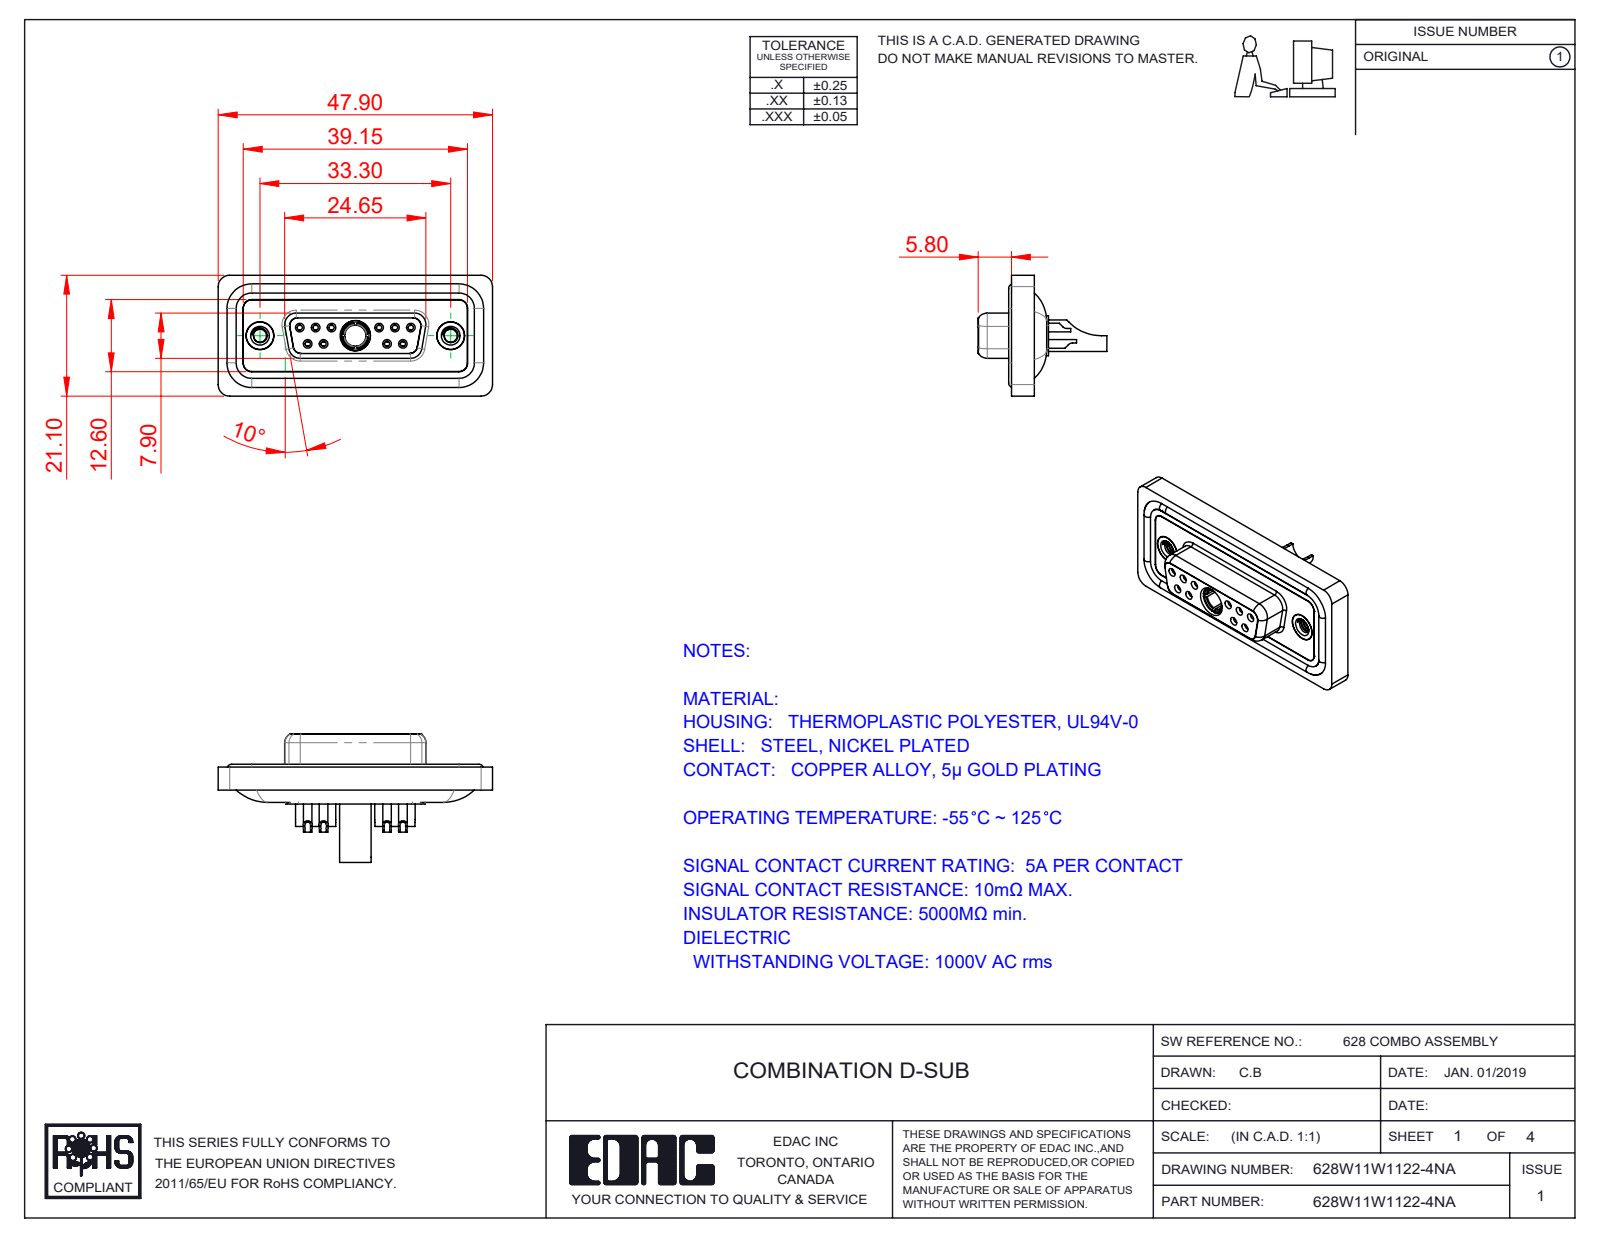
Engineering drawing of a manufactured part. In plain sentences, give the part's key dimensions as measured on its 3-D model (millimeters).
The part is named "628Combo Shell Rear_15 Contacts; 628Combo Shell Front_15 Contacts; Power Socket_40A SC; 628Combo Housing_11W1 (+5 more)". Its 3-D file was written by "SolidWorks 2020 (CONFIG_CONTROL_DESIGN)". It is 19 solids with 1012 faces: 306 planar, 424 cylindrical and 282 other. Overall it measures 47.9 by 22.45 by 21.1 millimeters. Its volume is 6 187 cubic millimeters and its surface area 10 270 square millimeters. Round holes: 10 of diameter 0.9, 10 of diameter 1, 10 of diameter 1.1, 10 of diameter 1.5, 10 of diameter 2, 6 of diameter 1.7, 4 of diameter 1.6, 3 of diameter 4.85, 2 of diameter 2.26, 2 of diameter 4, 2 of diameter 4.05, 2 of diameter 5. Round bosses or shafts: 10 of diameter 2.2, 10 of diameter 1.6, 2 of diameter 4.95, 2 of diameter 4.8, 1 of diameter 5.5, 1 of diameter 5.2, 1 of diameter 4.96, 1 of diameter 4.75. Partial cylindrical surfaces (rounded edges, fillets, slot ends): 22 of radius 1.5, 20 of radius 2, 12 of radius 1.35, 8 of radius 1.6, 6 of radius 1, 4 of radius 0.25, 4 of radius 0.5, 4 of radius 0.6. The main face-to-face distances are 0.4, 1.6, 1.8, 2.9, 0.5, 1.1, 5.65, 7.45, 6.6, 7.05. The hole center spacings are 3.16, 2.77, 13.85, 11.08, 16.62, 5.03, 5.04, 5.54.
